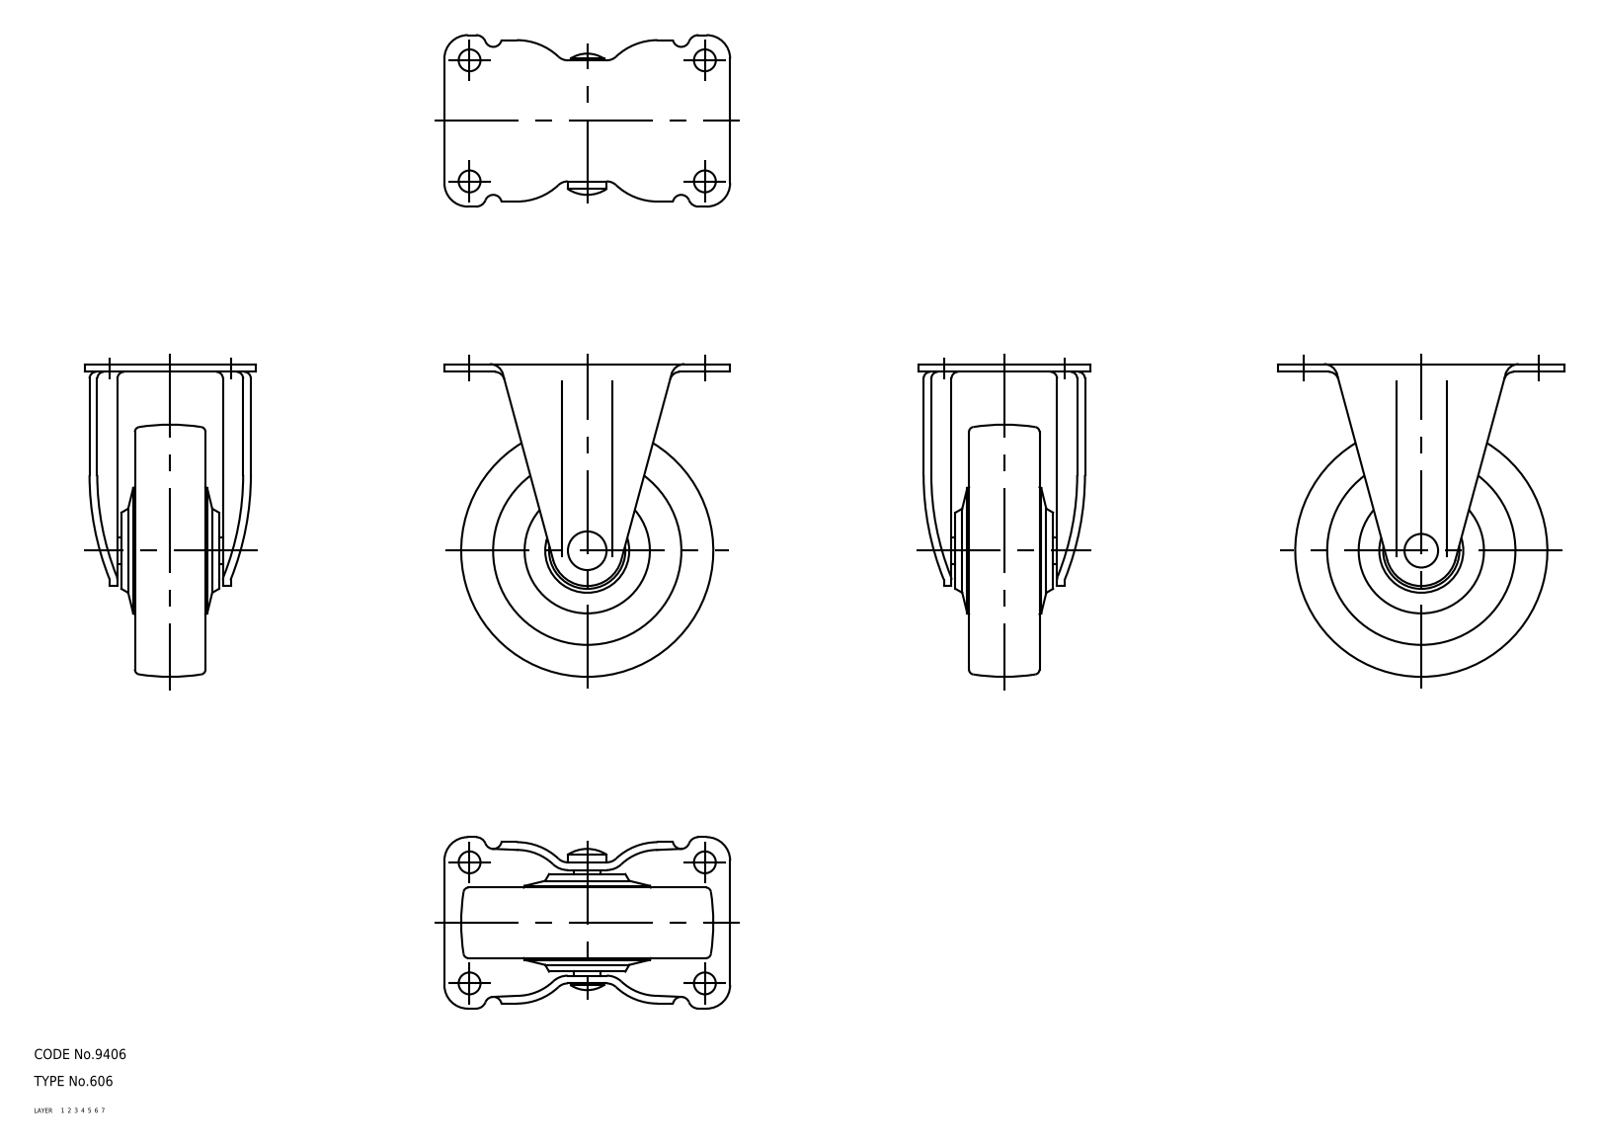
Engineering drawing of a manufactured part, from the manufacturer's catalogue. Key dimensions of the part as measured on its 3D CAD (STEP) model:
Part name (STEP PRODUCT): wheel; axle; No_606_16158_36
STEP written by: CADfix (AUTOMOTIVE_DESIGN)
Units: millimetres
Bodies: 3 solids, 150 faces (0 planar, 0 cylindrical, 150 other)
Overall size (bounding box): 93 × 85 × 51
Volume: 110 338 mm³ · Surface area: 33 370 mm²
